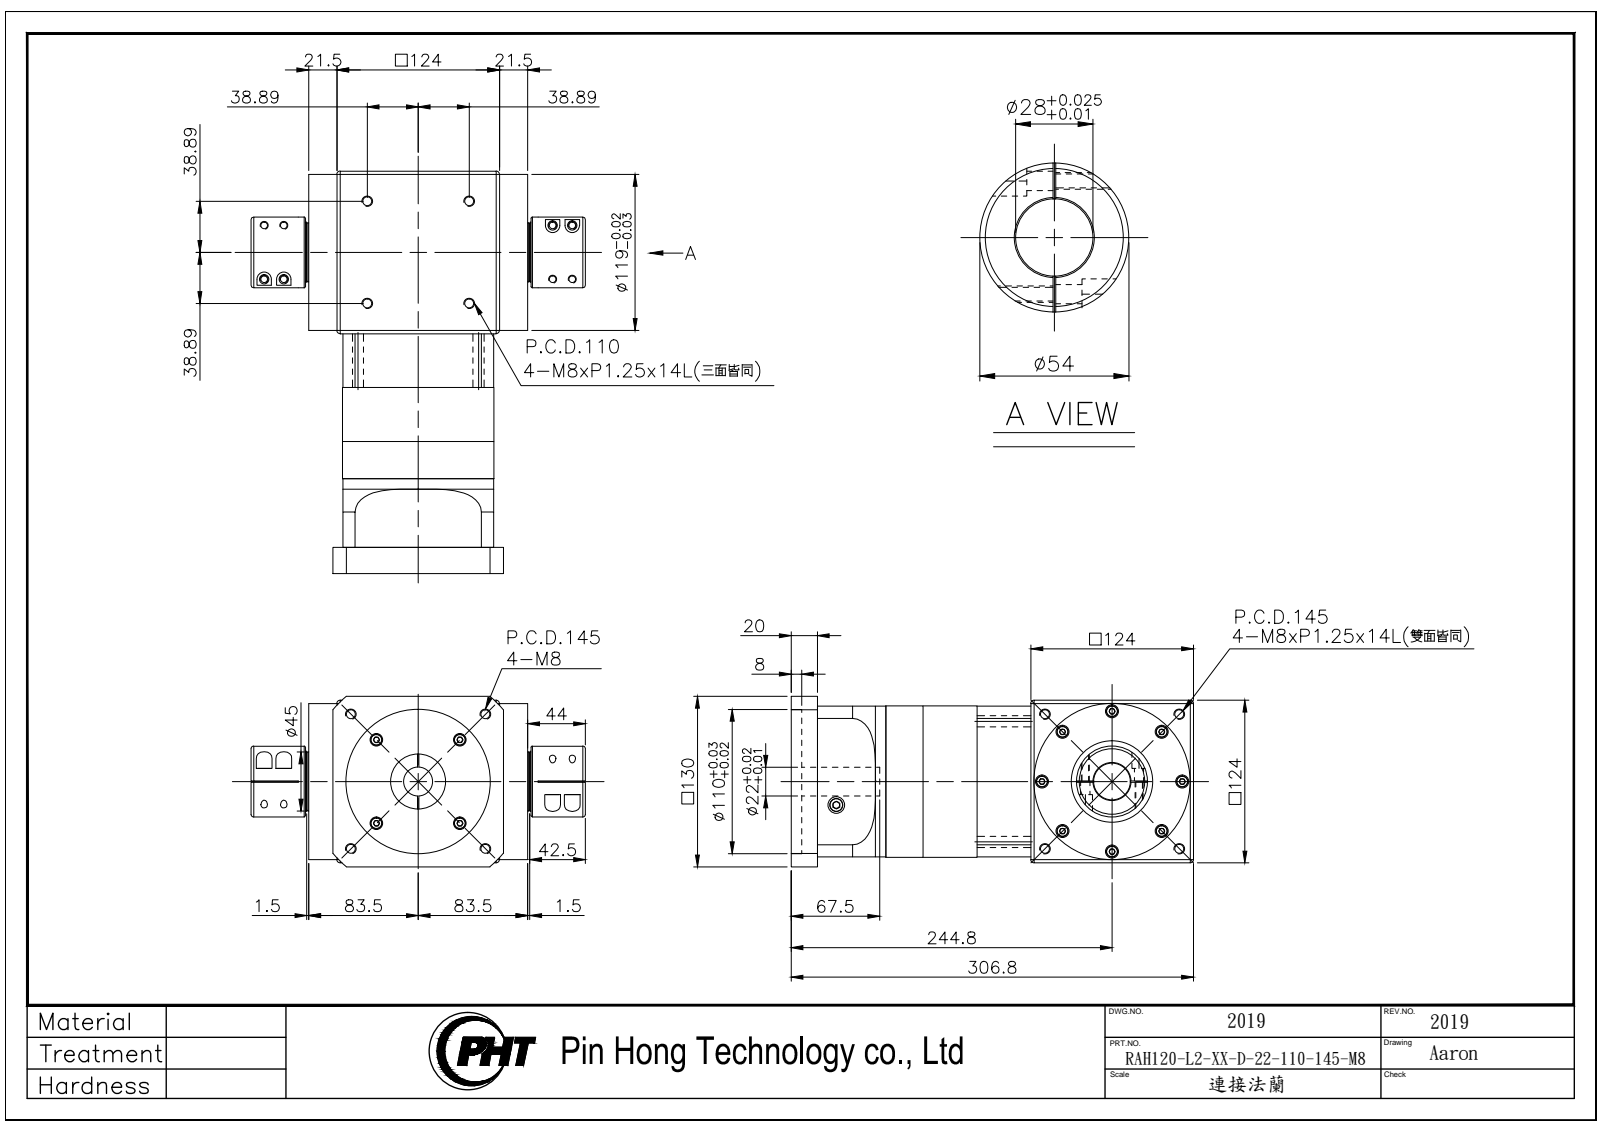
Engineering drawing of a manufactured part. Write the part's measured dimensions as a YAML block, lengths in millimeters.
part_name: "RAH120-L2-XX-D-22-110-145-M8_2019"
step_written_by: "SolidWorks 2016 (AUTOMOTIVE_DESIGN)"
units: millimeters
bodies: {solids: 3, faces: 1279, planar: 645, cylindrical: 410, other: 224}
overall_size: [306.8, 255, 130]
volume: 4410000
surface_area: 378381
round_holes:
  - {diameter: 6.8, count: 16}
  - {diameter: 9.5, count: 12}
  - {diameter: 5.4, count: 8}
  - {diameter: 7, count: 8}
  - {diameter: 9, count: 8}
  - {diameter: 14, count: 8}
  - {diameter: 5, count: 4}
  - {diameter: 5.5, count: 4}
  - {diameter: 8.5, count: 4}
  - {diameter: 12.7, count: 2}
  - {diameter: 22, count: 1}
  - {diameter: 28, count: 1}
round_bosses_or_shafts:
  - {diameter: 13, count: 12}
  - {diameter: 10.5, count: 8}
  - {diameter: 10, count: 8}
  - {diameter: 6, count: 8}
  - {diameter: 8.5, count: 4}
  - {diameter: 119, count: 1}
  - {diameter: 115.5, count: 1}
  - {diameter: 115, count: 1}
partial_cylinders:
  - {radius: 3.52, count: 8}
  - {radius: 5.5, count: 8}
  - {radius: 75, count: 1}
  - {radius: 85, count: 1}
  - {radius: 86.2, count: 1}
face_to_face_distances: [124, 4.5, 119.5, 3, 82.2, 115, 26, 206.2, 141, 127]
hole_center_spacings: [54, 10, 14.26, 15.71, 18.98, 24.68, 39.8, 51.28]
